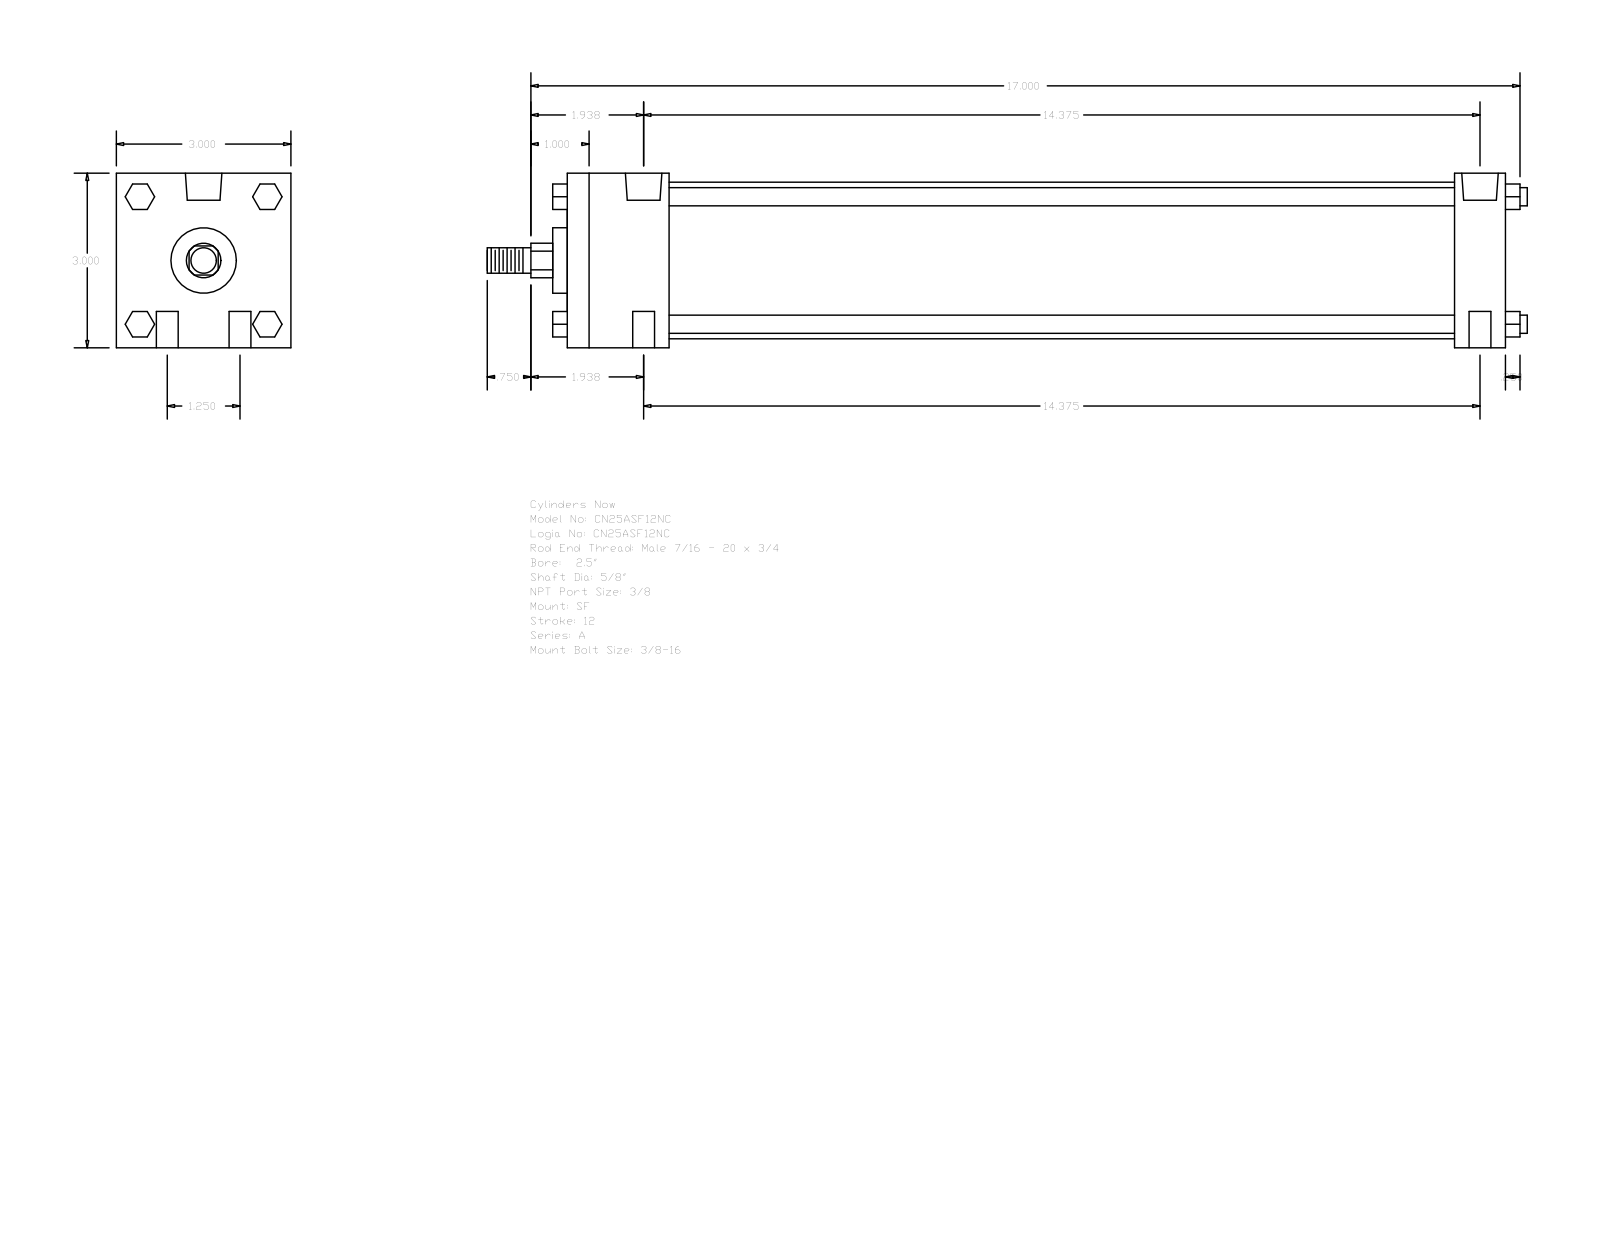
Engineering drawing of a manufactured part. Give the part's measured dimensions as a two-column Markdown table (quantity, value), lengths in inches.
| quantity | value |
| --- | --- |
| part name | A_SF__0250_0.625 |
| STEP written by | GSSL Pune (CONFIG_CONTROL_DESIGN) |
| units | inches |
| bodies | 0 solids, 124 faces (94 planar, 30 cylindrical, 0 other) |
| overall size | 17.875 × 3 × 3 |
| round holes (diameter × count) | 0.375 × 4, 0.219 × 2, 0.627 × 2 |
| round bosses / shafts (diameter × count) | 0.313 × 4, 2.69 × 1, 1.125 × 1, 0.625 × 1, 0.437 × 1 |
| partial cylindrical surfaces (radius × count) | 0.297 × 1 |
| main face-to-face distances | 3, 16.125, 1.75, 15.25, 0.875, 13.5, 14.375, 0.25, 16.375, 2 |
| hole center spacings | 0.625, 14.389, 14.375, 1.25, 14.43, 14.563 |
